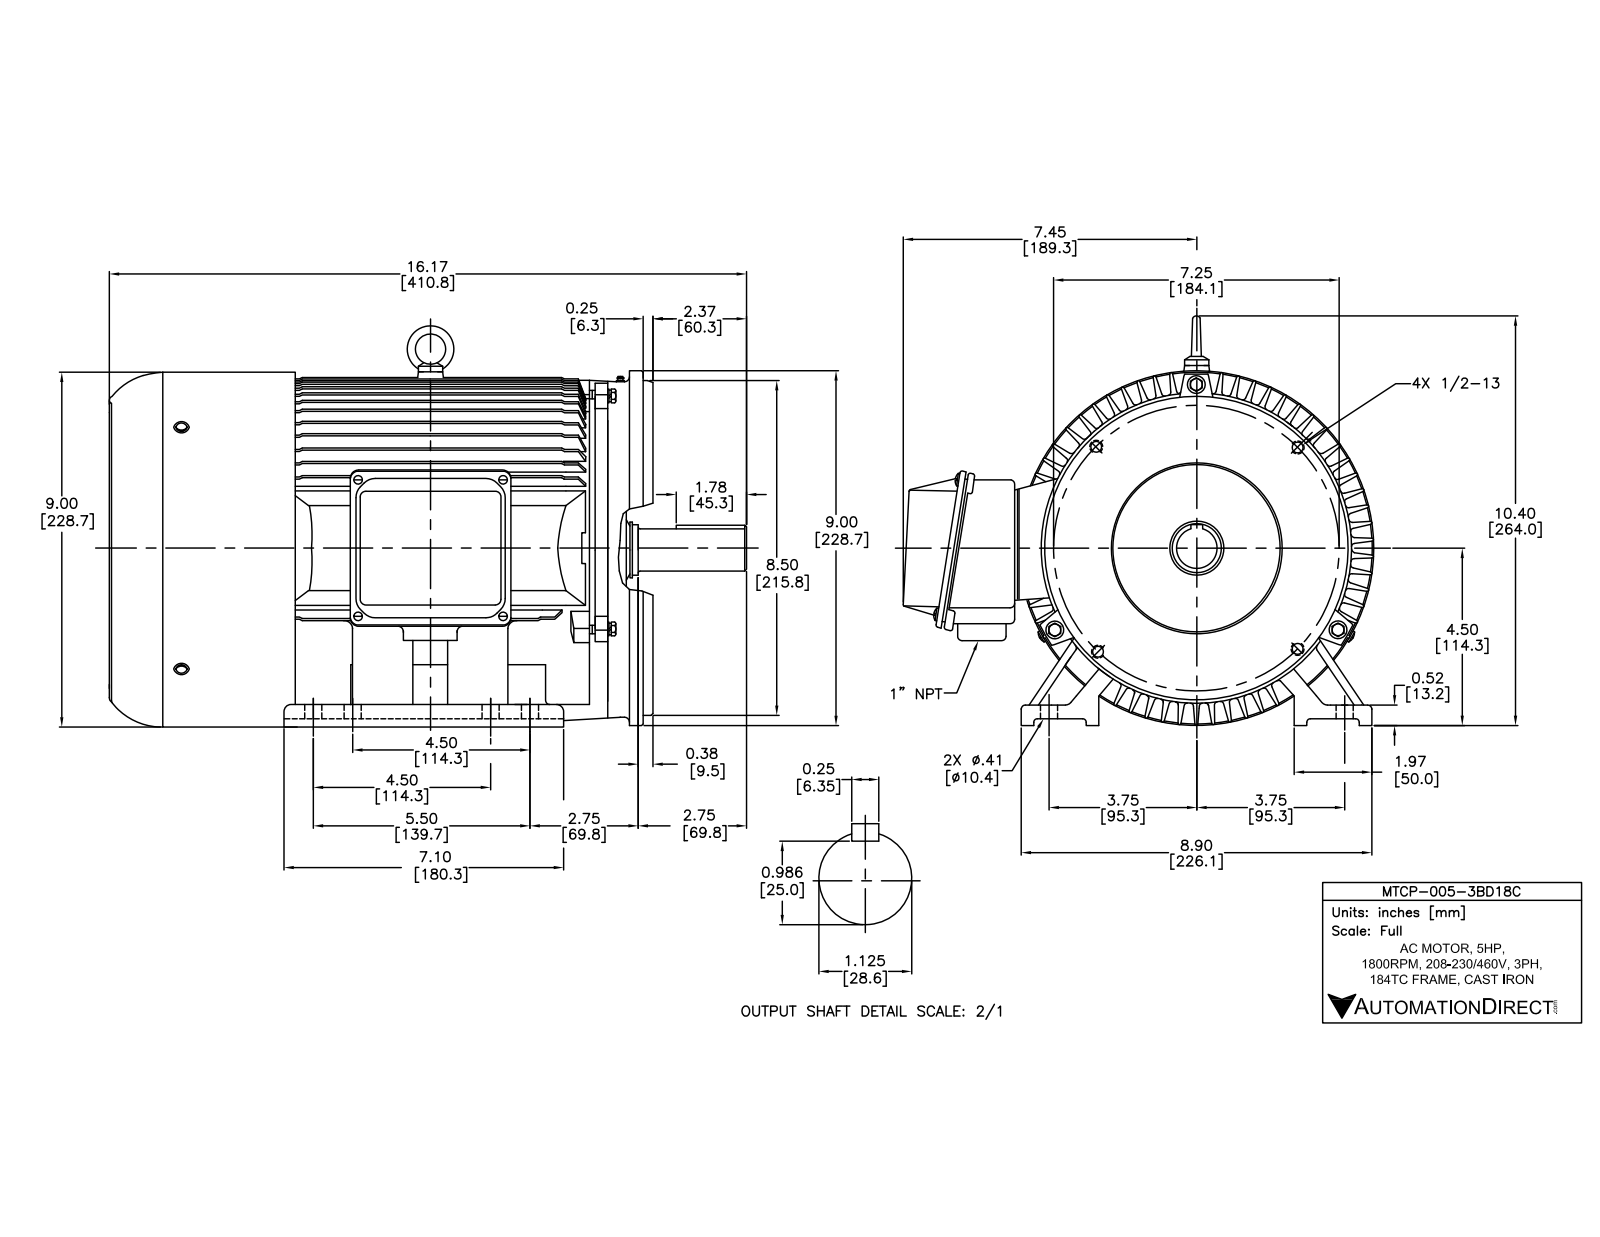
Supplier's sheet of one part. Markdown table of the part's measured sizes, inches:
| quantity | value |
| --- | --- |
| part name | plain washers-chamfered--normal series-a gb_GB_FASTENER_WASHER_SWCA 8; MTCP184TC; spring lock washers--normal type gb_GB_FASTENER_WASHER_SW 8; plain washers-chamfered--normal series-a gb_GB_FASTENER_WASHER_SWCA 5 (+6 more) |
| STEP written by | SolidWorks 2017 (AUTOMOTIVE_DESIGN) |
| units | inches |
| bodies | 47 solids, 2420 faces (690 planar, 888 cylindrical, 842 other) |
| overall size | 16.165 × 11.867 × 10.449 |
| volume | 196.6 in³ |
| surface area | 1 637 in² |
| round holes (diameter × count) | 0.228 × 15, 0.165 × 11, 0.413 × 8, 0.268 × 4, 0.313 × 4, 0.422 × 4, 0.209 × 3, 0.213 × 3, 0.331 × 3, 0.342 × 3, 0.394 × 3, 0.866 × 3 |
| round bosses / shafts (diameter × count) | 0.197 × 11, 0.315 × 7, 0.63 × 3, 0.507 × 3, 0.394 × 3, 8.898 × 1, 8.638 × 1, 8.5 × 1 |
| partial cylindrical surfaces (radius × count) | 0.039 × 140, 0.02 × 67, 0.079 × 59, 0.118 × 35, 0.049 × 33, 0.276 × 22, 0.013 × 16, 0.315 × 11 |
| main face-to-face distances | 0.197, 0.236, 0.047, 10.48, 0.512, 11.953, 11.906, 0.276, 13.378, 13.331 |
| hole center spacings | 2.677, 4.666, 3.937, 0.688, 1, 2.678, 2.937, 3.625 |
